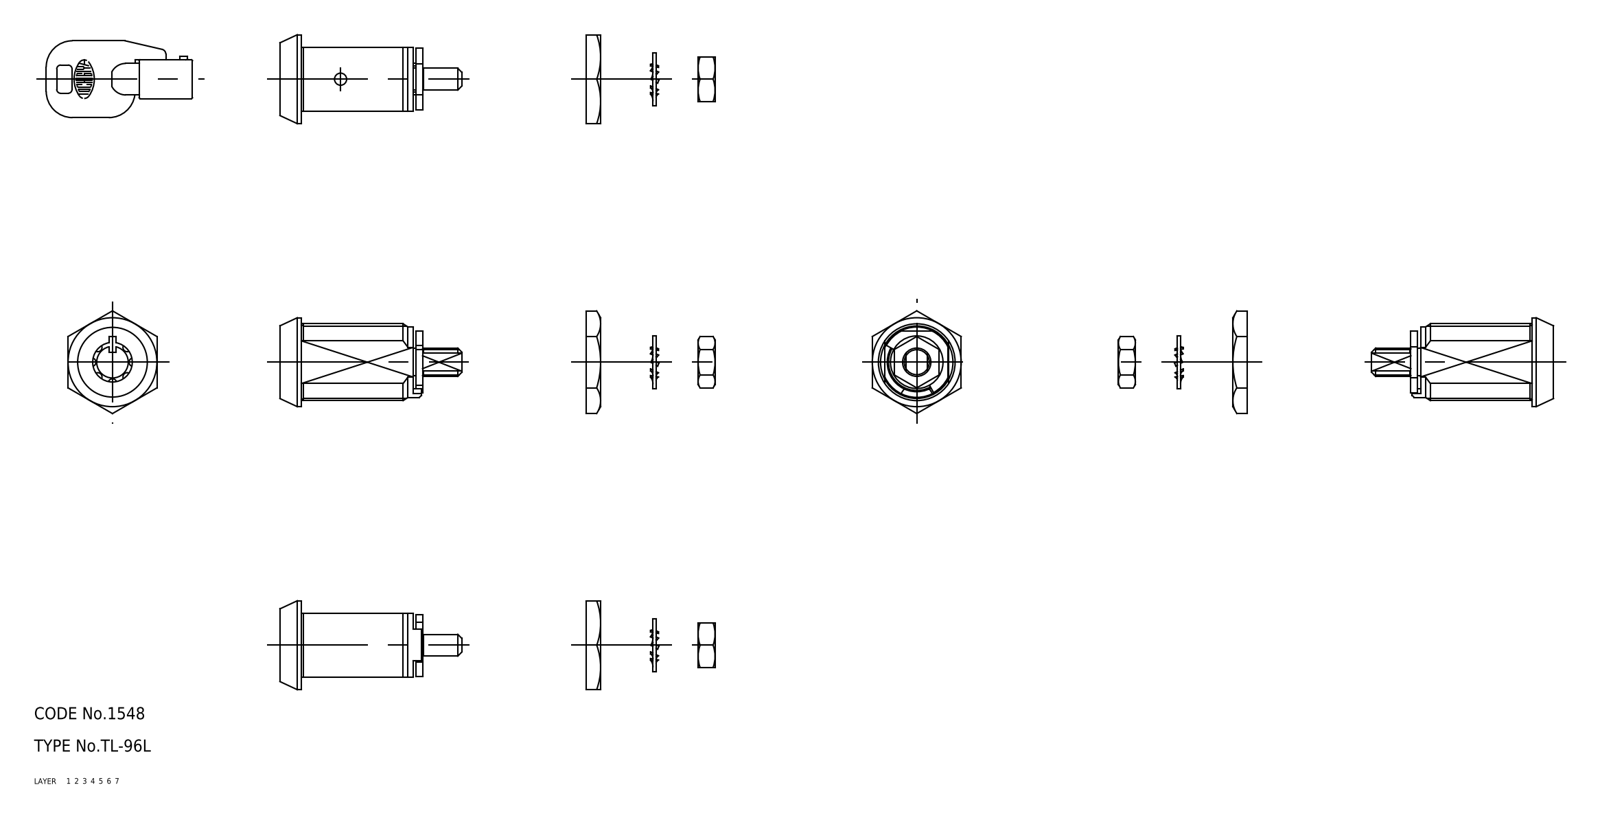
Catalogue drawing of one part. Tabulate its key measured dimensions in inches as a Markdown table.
| quantity | value |
| --- | --- |
| part name | nut_B; nut_A; lock; key (+1 more) |
| STEP written by | CADfix (AUTOMOTIVE_DESIGN) |
| units | inches |
| bodies | 4 solids, 148 faces (0 planar, 0 cylindrical, 148 other) |
| overall size | 4.567 × 1 × 0.866 |
| volume | 0.696 in³ |
| surface area | 10.53 in² |
